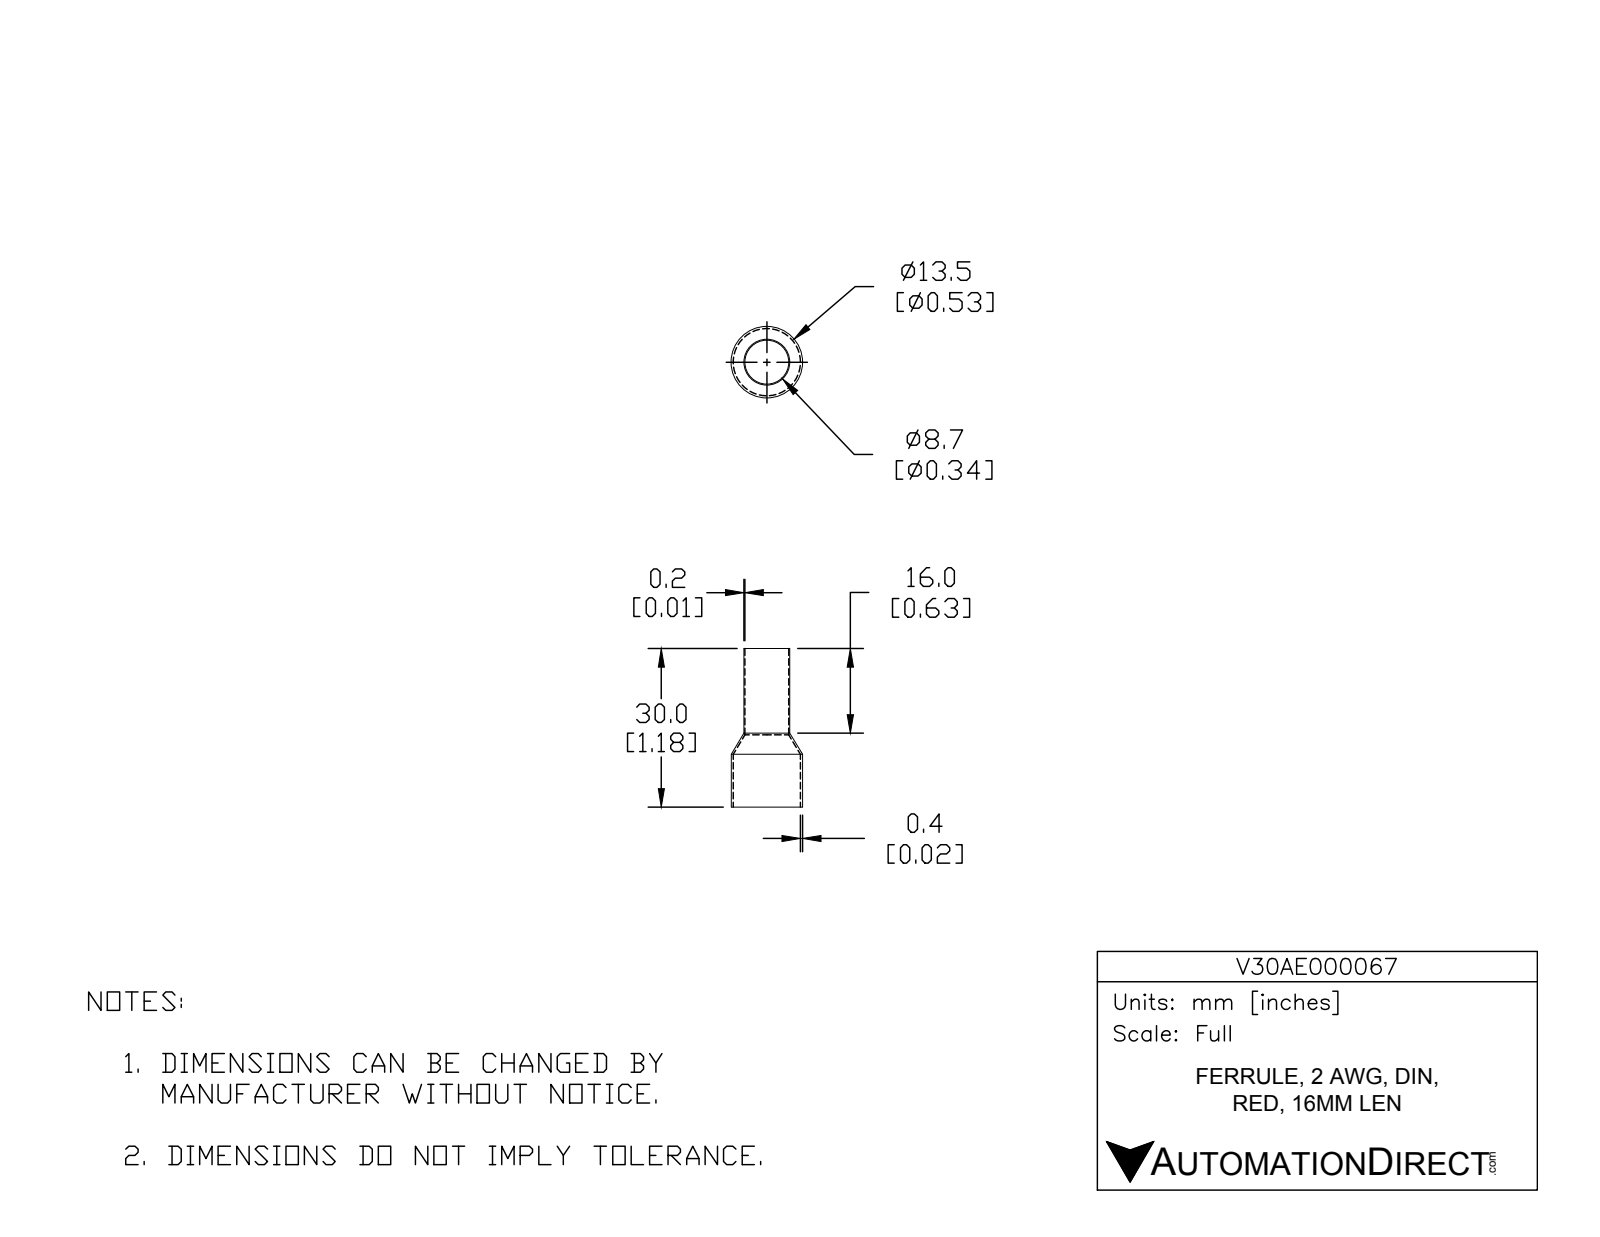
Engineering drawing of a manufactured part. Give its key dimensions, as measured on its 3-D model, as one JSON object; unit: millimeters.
{"part_name": "V30AE000067", "step_written_by": "SolidWorks 2017 (AUTOMOTIVE_DESIGN)", "units": "millimeters", "bodies": {"solids": 1, "faces": 14, "planar": 2, "cylindrical": 8, "other": 4}, "overall_size": [30, 13.5, 13.5], "volume_mm3": 303, "surface_area_mm2": 2012, "round_holes": [[8.3, 1], [12.7, 1]], "round_bosses_or_shafts": [[13.5, 1], [8.7, 1]], "face_to_face_distances": [30]}
